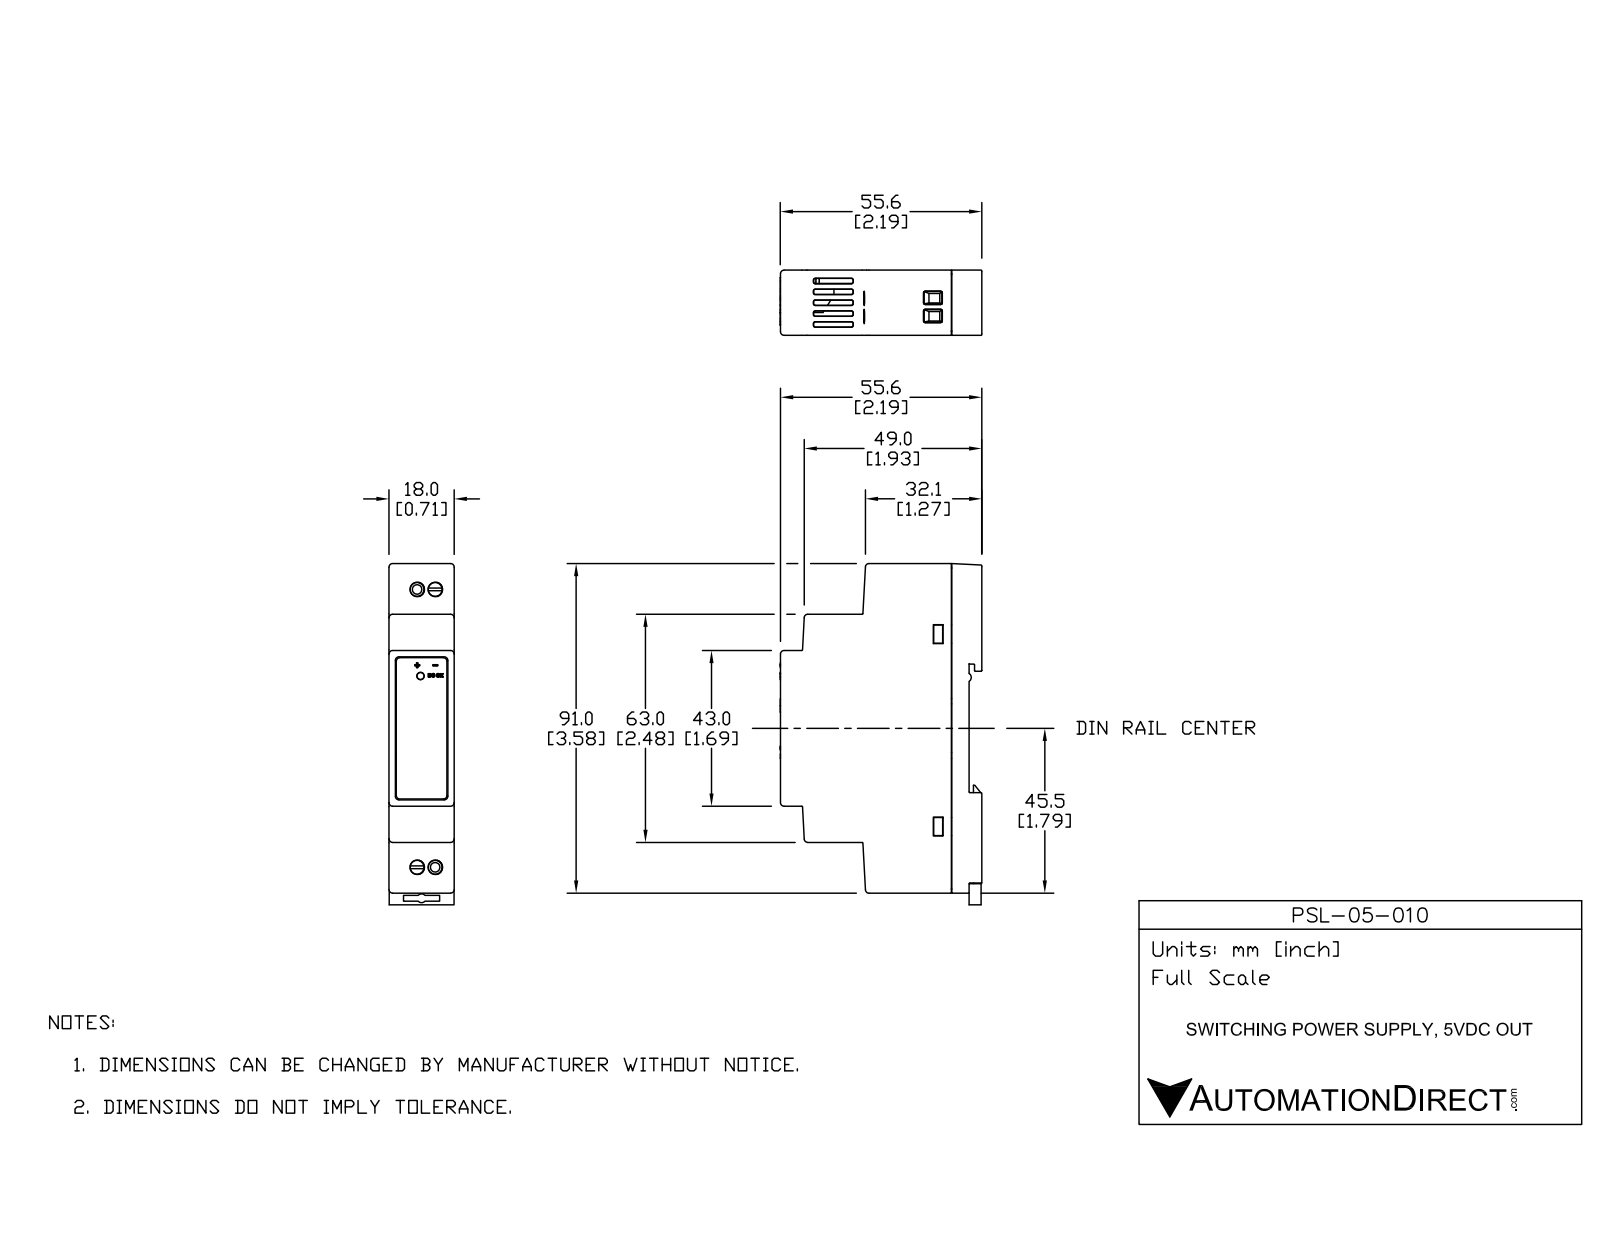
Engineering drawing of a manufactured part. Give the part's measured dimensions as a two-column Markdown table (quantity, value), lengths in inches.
| quantity | value |
| --- | --- |
| part name | PSL-05-010 |
| STEP written by | SolidWorks 2017 (AUTOMOTIVE_DESIGN) |
| units | inches |
| bodies | 12 solids, 926 faces (579 planar, 267 cylindrical, 80 other) |
| overall size | 3.709 × 2.189 × 0.709 |
| volume | 1.6 in³ |
| surface area | 61.41 in² |
| round holes (diameter × count) | 0.103 × 4, 0.157 × 4, 0.159 × 4, 0.118 × 1, 0.161 × 1 |
| round bosses / shafts (diameter × count) | 0.151 × 2, 0.037 × 2 |
| partial cylindrical surfaces (radius × count) | 0.008 × 87, 0.02 × 58, 0.039 × 35, 0.004 × 17, 0.031 × 8, 0.059 × 6, 0.122 × 2, 0.048 × 1 |
| main face-to-face distances | 0.709, 0.039, 0.524, 0.185, 0.563, 0.146, 0.051, 0.228, 0.177, 0.063 |
| hole center spacings | 3.02, 3.026, 0.197, 0.195, 0.199, 0.942, 2.079, 2.085 |
